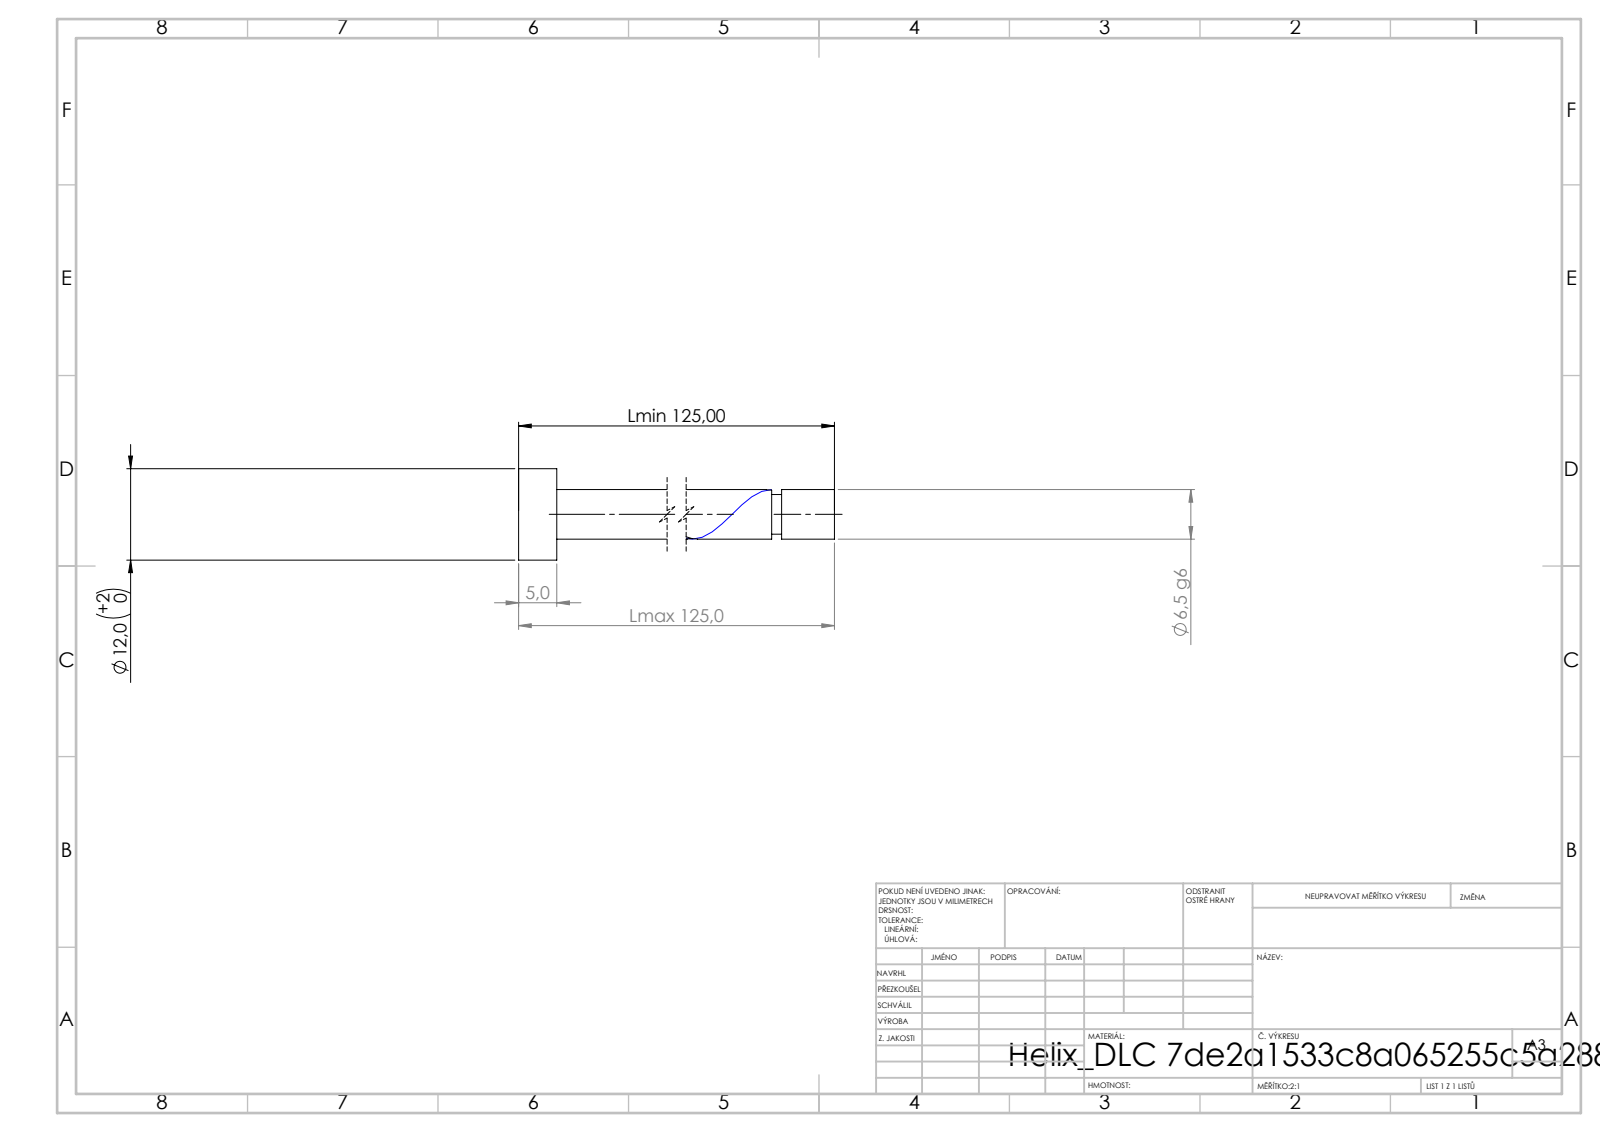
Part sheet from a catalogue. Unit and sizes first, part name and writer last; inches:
Units: inches
Overall size (bounding box): 4.921 × 0.472 × 0.472
Round bosses / shafts (diameter × count): ⌀0.472 ×1, ⌀0.256 ×1, ⌀0.205 ×1
Main face-to-face distances: 0.197, 4.921, 4.724, 4.648, 4.451, 0.273, 4.597, 4.4, 0.051, 0.324
Volume: 0.274 in³ · Surface area: 4.565 in²
Bodies: 1 solid, 21 faces (6 planar, 14 cylindrical, 1 other)
STEP written by: SolidWorks 2019 (CONFIG_CONTROL_DESIGN)
